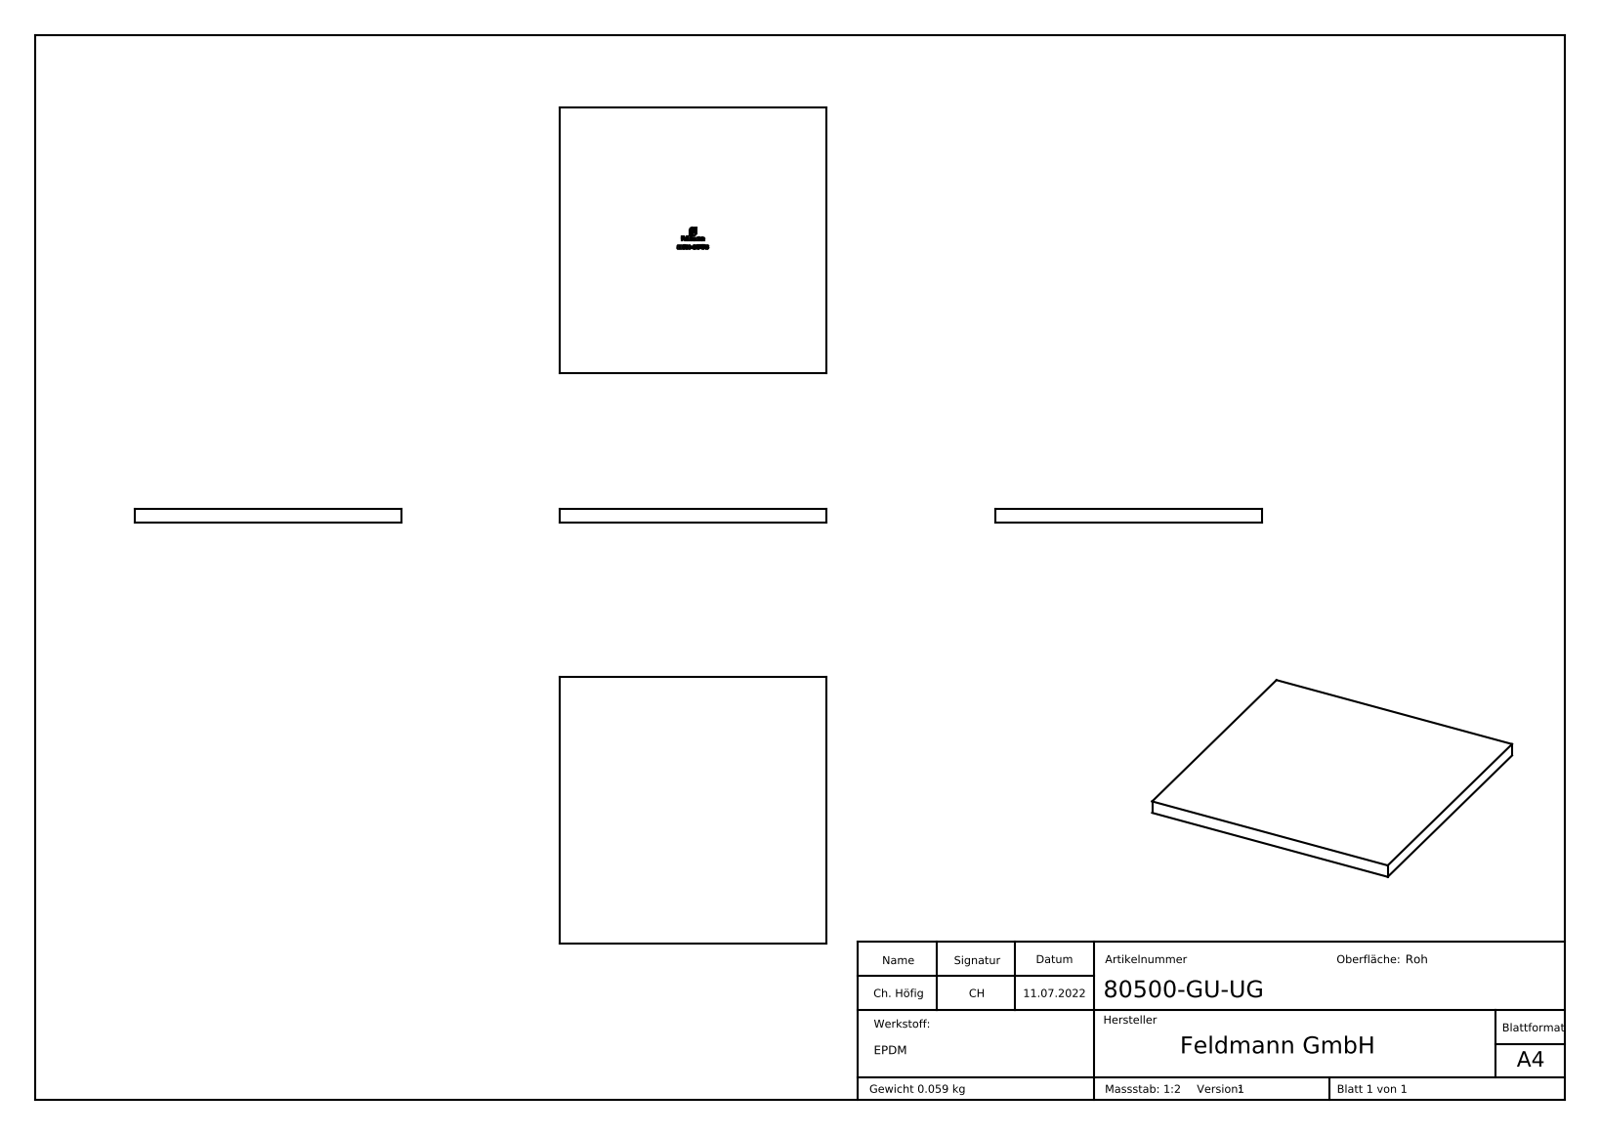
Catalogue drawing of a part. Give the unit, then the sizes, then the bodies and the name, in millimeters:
Units: millimetres
Overall size (bounding box): 100 × 100 × 5
Main face-to-face distances: 5, 100, 4.9, 2.2, 0.58, 1.82, 3.27, 0.68, 2.97, 2.7
Volume: 49 999 mm³ · Surface area: 22 014 mm²
Bodies: 1 solid, 296 faces (144 planar, 0 cylindrical, 152 other)
Part name (STEP PRODUCT): 80500-GU-UG
STEP written by: SolidWorks 2018 (CONFIG_CONTROL_DESIGN)
